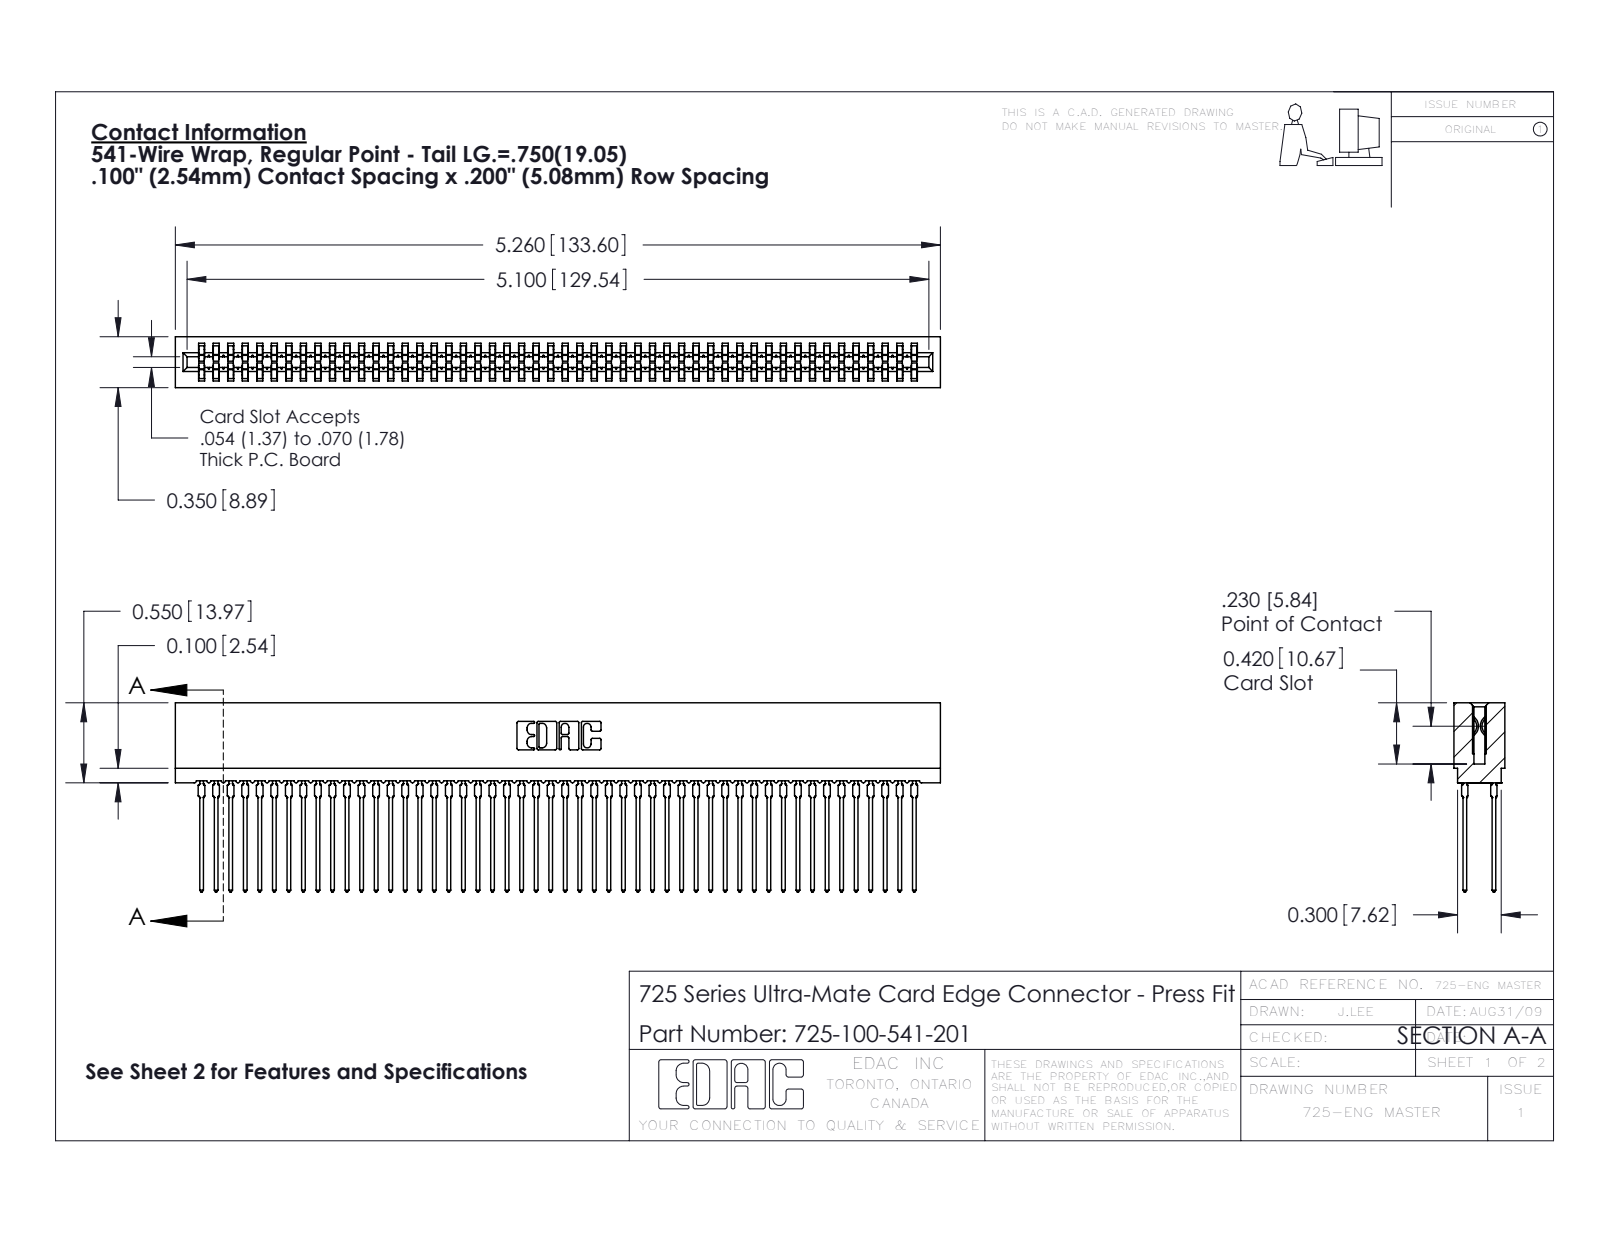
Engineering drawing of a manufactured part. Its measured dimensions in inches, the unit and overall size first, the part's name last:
Units: inches
Overall size (bounding box): 5.26 × 1.3 × 0.35
Partial cylindrical surfaces — rounded edges, fillets, slot ends (radius × count): R0.021 ×200, R0.015 ×100, R0.01 ×22, R0.005 ×8, R0.011 ×8, R0.007 ×6, R0.031 ×6, R0.026 ×3
Main face-to-face distances: 0.063, 0.287, 0.2, 0.087, 0.263, 0.025, 0.35, 0.212, 0.138, 0.076
Volume: 0.674 in³ · Surface area: 39.48 in²
Bodies: 101 solids, 9045 faces (4655 planar, 1790 cylindrical, 2600 other)
Part name (STEP PRODUCT): 745-292-001_541; 725-100-541-201; 725 Part_Insulator Option - 01
STEP written by: SolidWorks 2016 (CONFIG_CONTROL_DESIGN)
